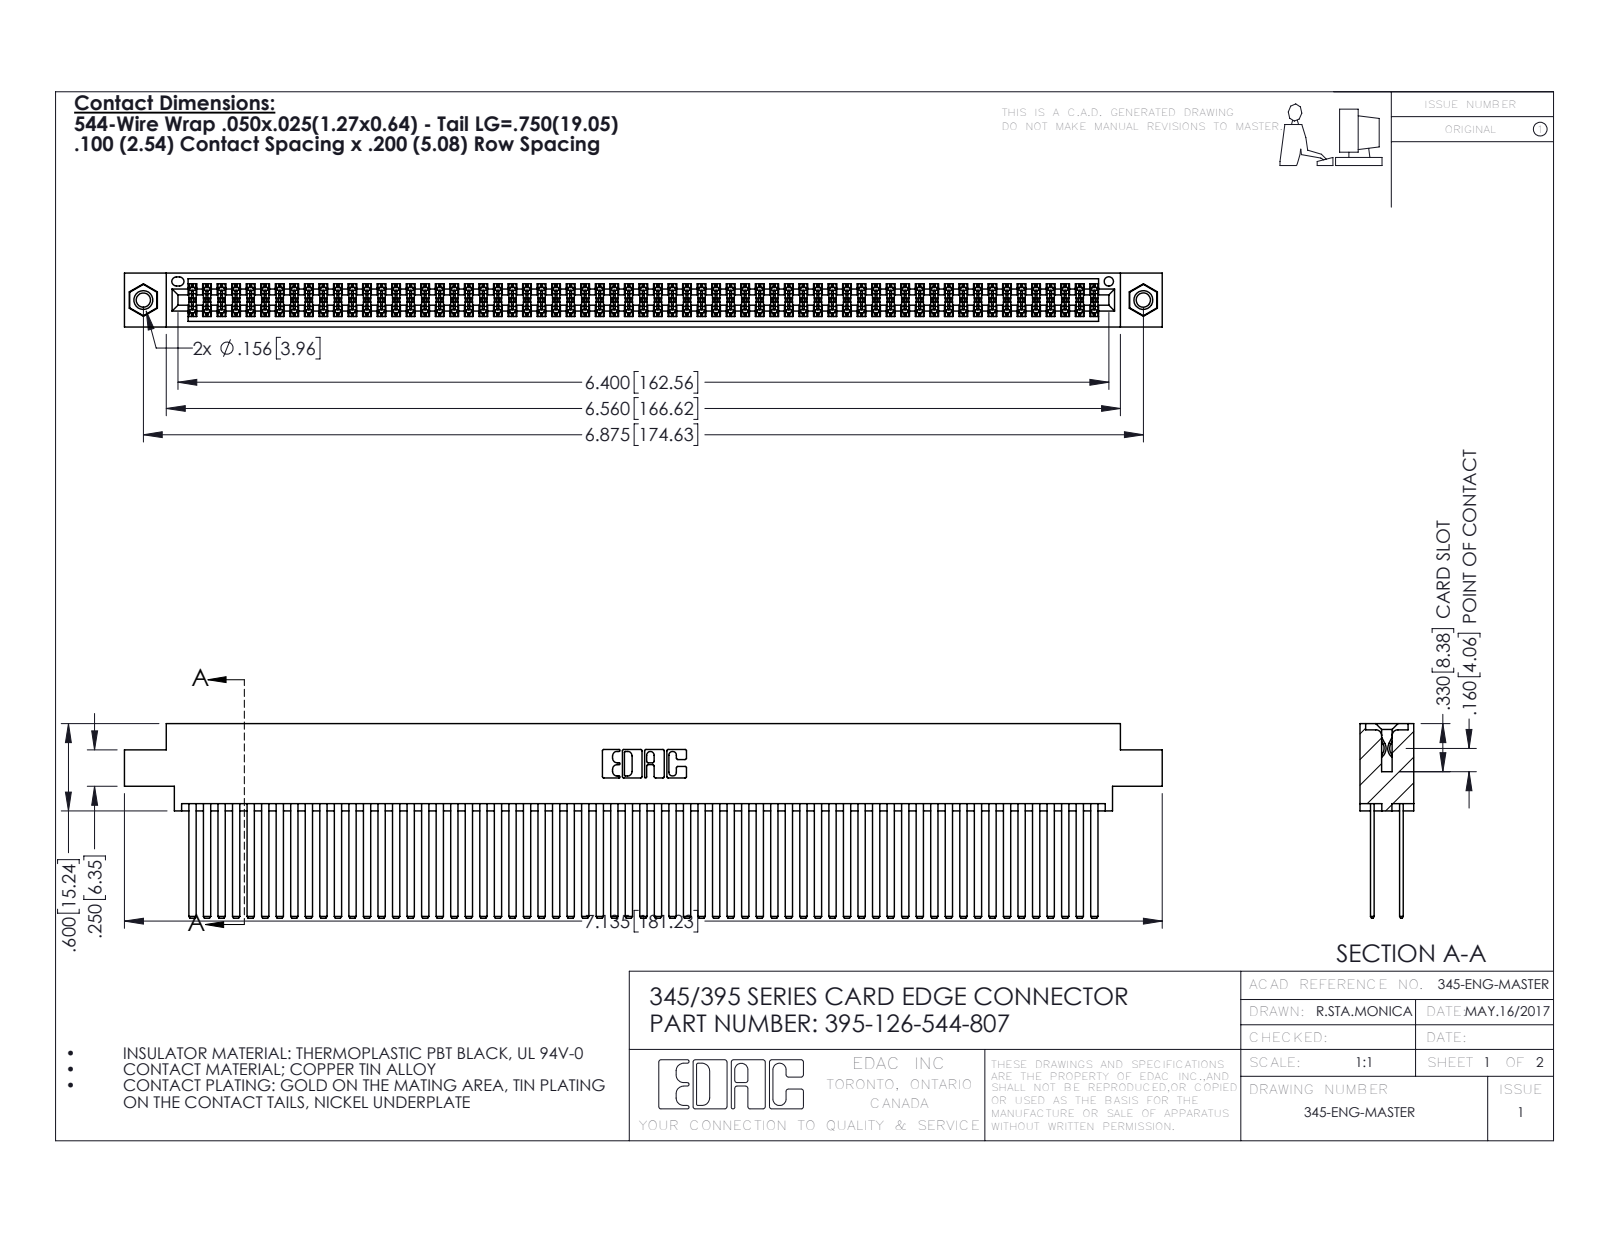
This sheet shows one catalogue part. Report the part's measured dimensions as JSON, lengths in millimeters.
{"part_name": "395-126-544-807; 345-292-001_345-293-144; 345-250-001_345-250-005-103; 345 Part_0.170 Offset - 0.156 Dia-TI", "step_written_by": "SolidWorks 2016 (CONFIG_CONTROL_DESIGN)", "units": "millimeters", "bodies": {"solids": 129, "faces": 5734, "planar": 3770, "cylindrical": 1948, "other": 16}, "overall_size": [181.2, 34, 9.4], "volume_mm3": 19440, "surface_area_mm2": 34490, "round_holes": [[2.5, 2], [3.2, 2], [4, 2], [1.6, 1]], "round_bosses_or_shafts": [[3.9, 2]], "partial_cylinders_radius": [[0.2, 189], [0.3, 22], [0.2, 6], [0.8, 6], [0.7, 3], [0.4, 2], [0.5, 2], [0.6, 2]], "face_to_face_distances": [5.1, 0.6, 1.8, 2.5, 6.9, 7.6, 5.7, 4.4, 9.4, 3.8], "hole_center_spacings": [6.9, 168.6, 174.6]}
